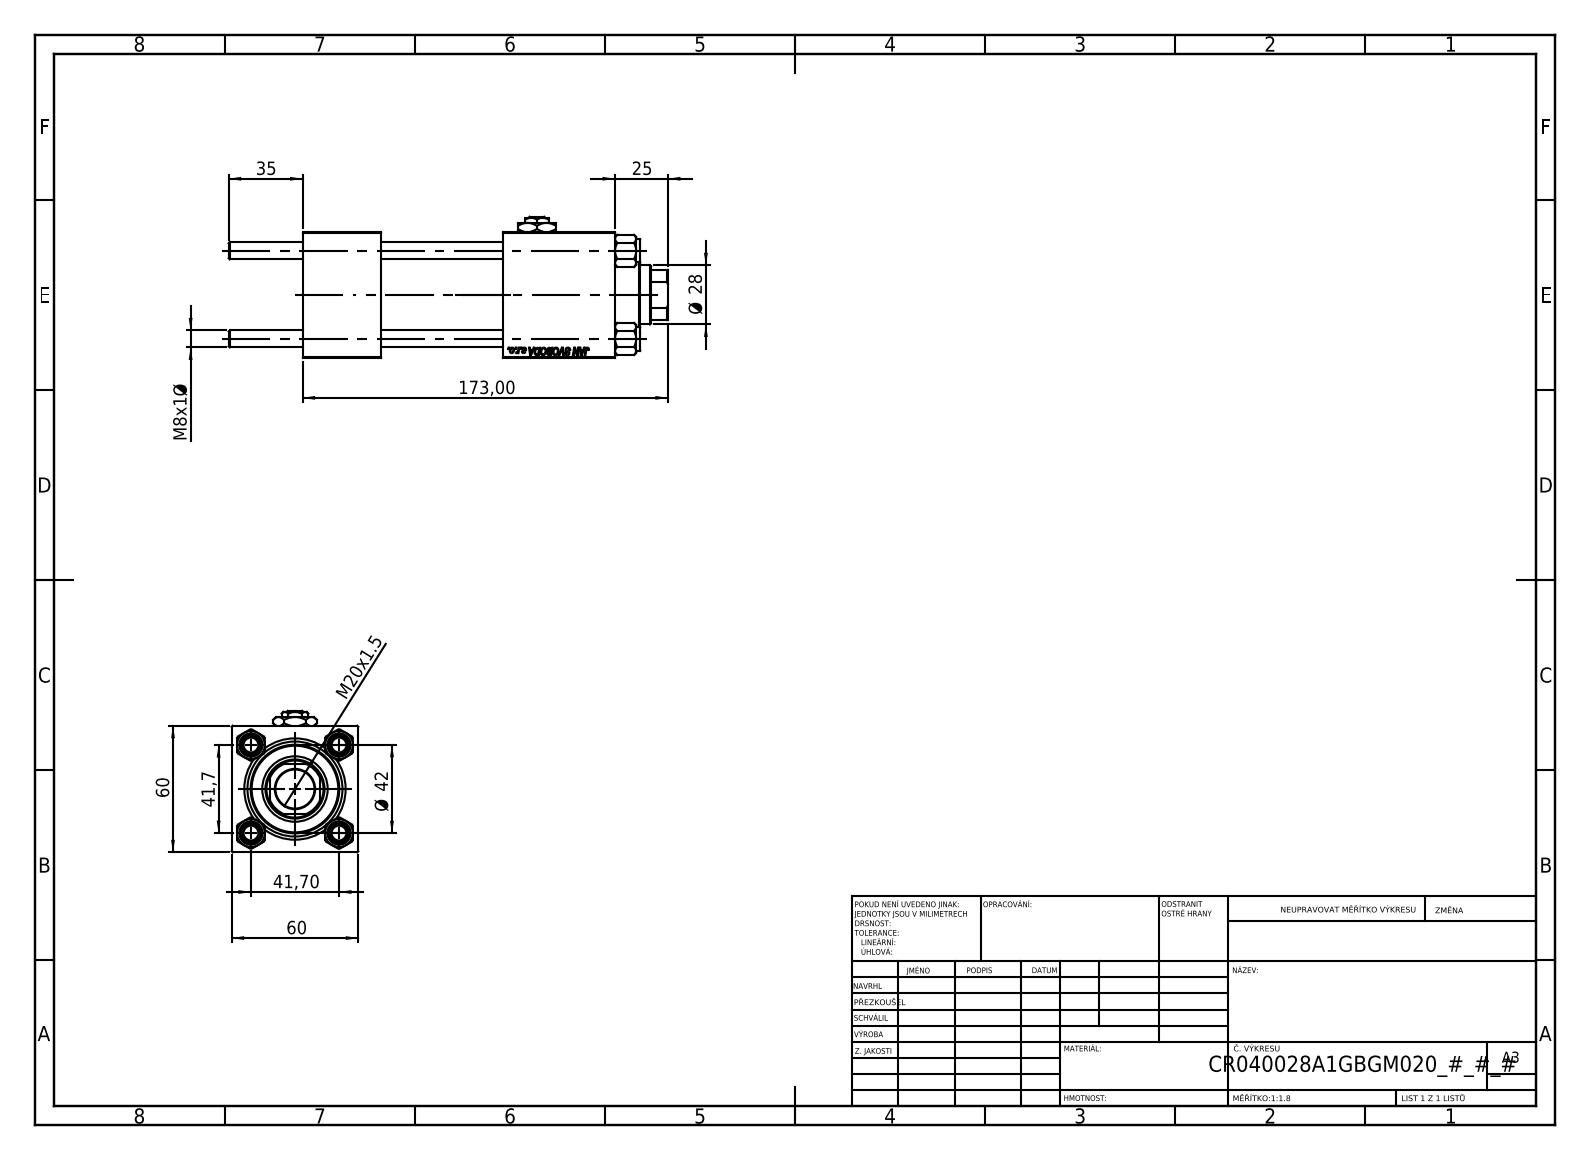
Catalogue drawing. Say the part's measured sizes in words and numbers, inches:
The part is named "NUT_M5; V215CR_VCP; Zatka_pro_OIL_PORT; V215_VC_A (+2 more)". Its 3-D file was written by "SolidWorks 2019 (CONFIG_CONTROL_DESIGN)". It is 12 solids with 1182 faces: 544 planar, 82 cylindrical and 556 other. Overall it measures 8.189 by 2.638 by 2.362 inches. Its volume is 26.46 cubic inches and its surface area 188.1 square inches. Round holes: 4 of diameter 0.315, 2 of diameter 0.276, 2 of diameter 0.656, 2 of diameter 0.945, 1 of diameter 0.728, 1 of diameter 1.102, 1 of diameter 1.22, 1 of diameter 1.575, 1 of diameter 1.772. Round bosses or shafts: 4 of diameter 0.433, 1 of diameter 1.811, 1 of diameter 1.654. Partial cylindrical surfaces (rounded edges, fillets, slot ends): 1 of radius 0.531. The main face-to-face distances are 2.362, 1.457, 2.283, 3.74, 2.087, 5.827, 4.37, 4.697, 3.24, 0.957. The hole center spacings are 1.161, 1.642, 2.322, 3.642.
